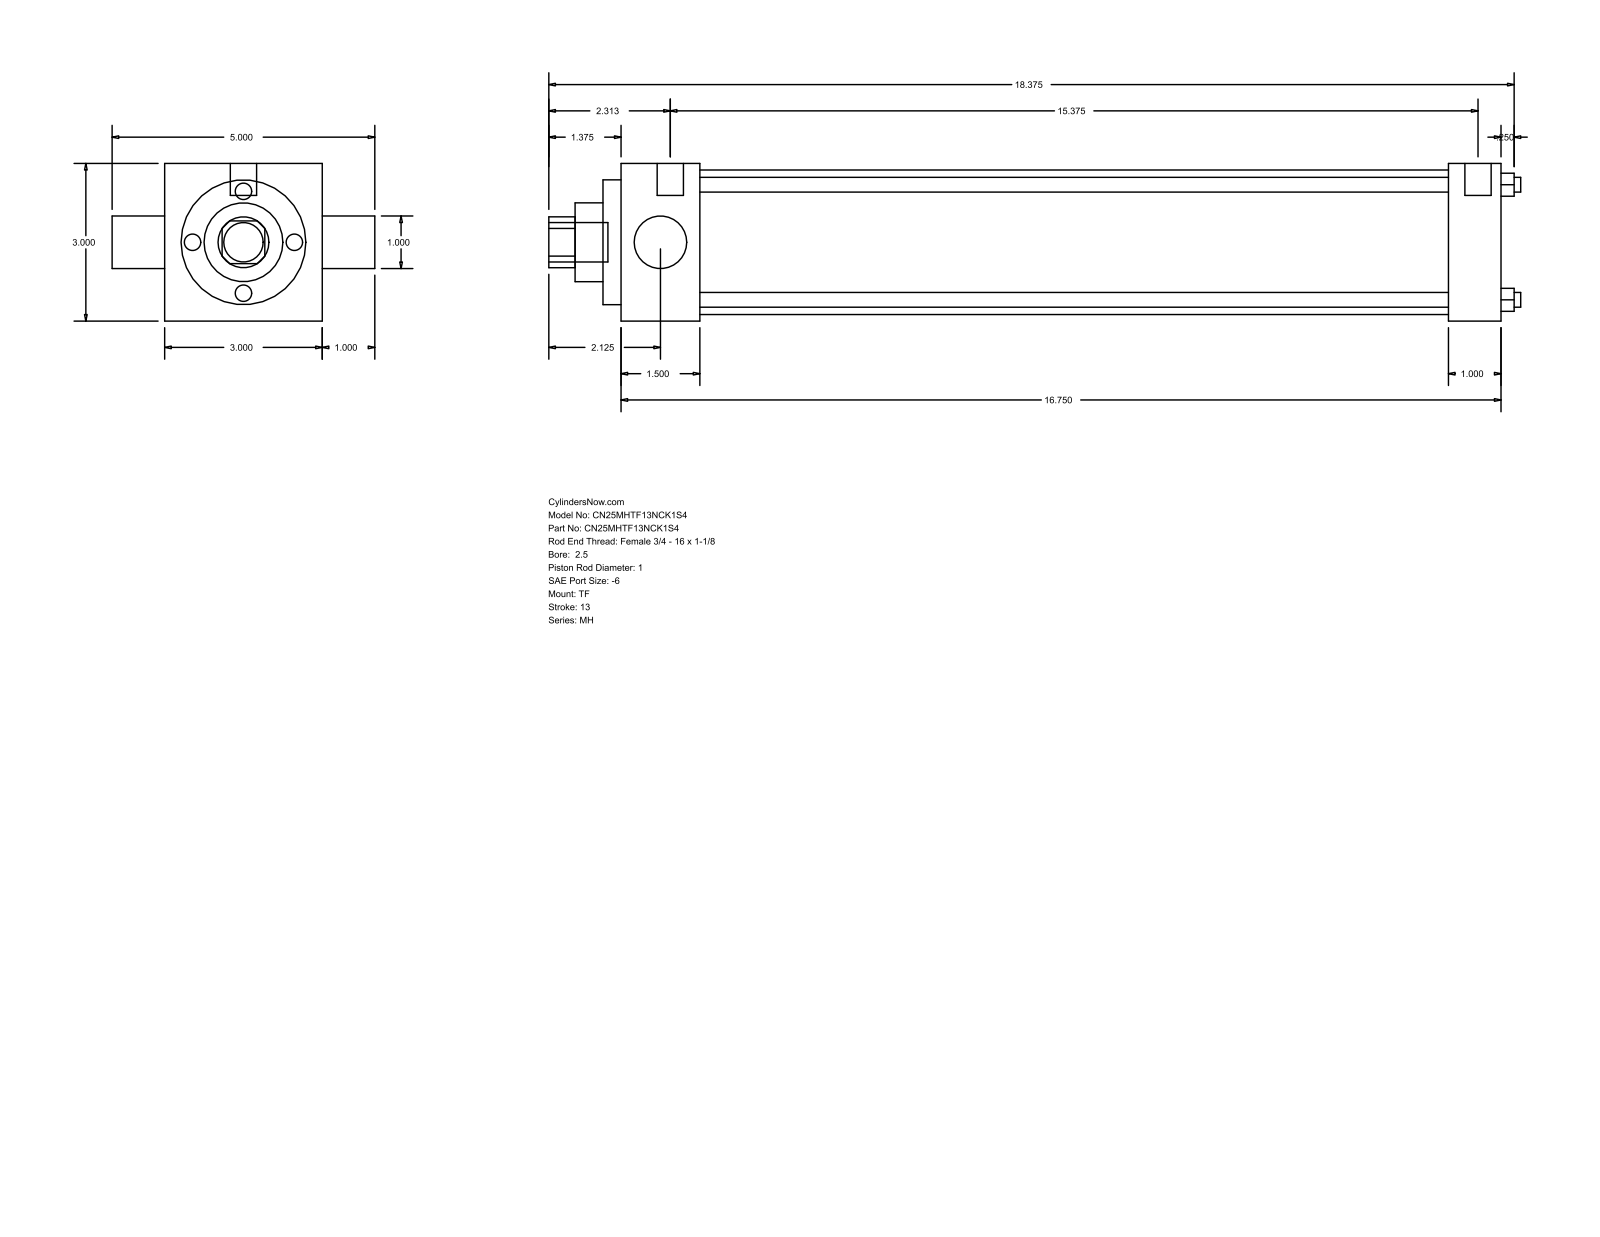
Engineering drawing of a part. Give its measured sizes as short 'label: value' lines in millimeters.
name: MH_TF__0250_1
written by: GSSL Pune (CONFIG_CONTROL_DESIGN)
unit: mm
bodies: 0 solids, 86 faces (61 planar, 25 cylindrical, 0 other)
size: 469.9 × 127 × 76.2
holes: 4× ⌀7.14, 2× ⌀25.4, 1× ⌀38.1, 1× ⌀60.33, 1× ⌀69.85
bosses: 3× ⌀5.56, 2× ⌀12.7, 1× ⌀19.05
rounds: 1× R12.29
face distances: 76.2, 425.46, 25.4, 38.11, 387.35, 400.06, 361.95, 8.73, 46.84, 408.79
hole spacings: 39.33, 55.62, 78.66
